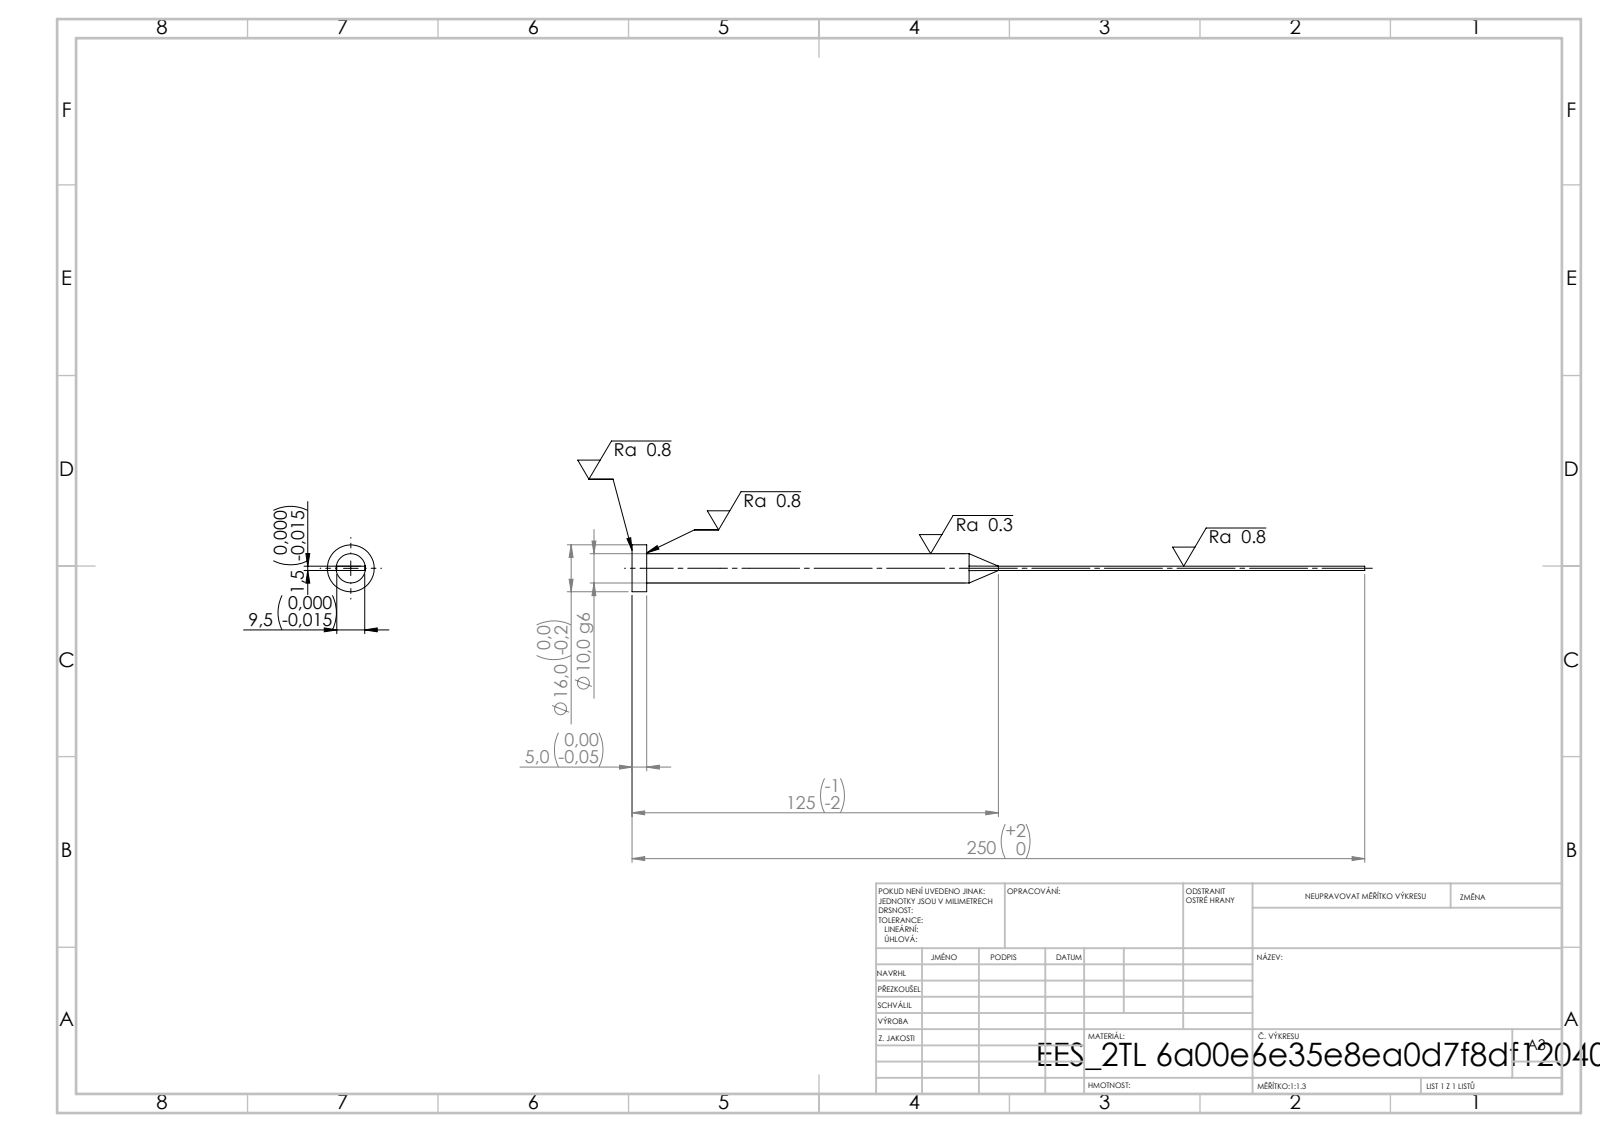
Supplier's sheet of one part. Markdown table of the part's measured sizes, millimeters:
| quantity | value |
| --- | --- |
| STEP written by | SolidWorks 2019 (CONFIG_CONTROL_DESIGN) |
| units | millimeters |
| bodies | 1 solid, 15 faces (7 planar, 4 cylindrical, 4 other) |
| overall size | 250 × 16 × 16 |
| volume | 11 864 mm³ |
| surface area | 7 059 mm² |
| round bosses / shafts (diameter × count) | 16 × 1, 10 × 1 |
| main face-to-face distances | 1.5, 9.5, 5, 250, 245 |
